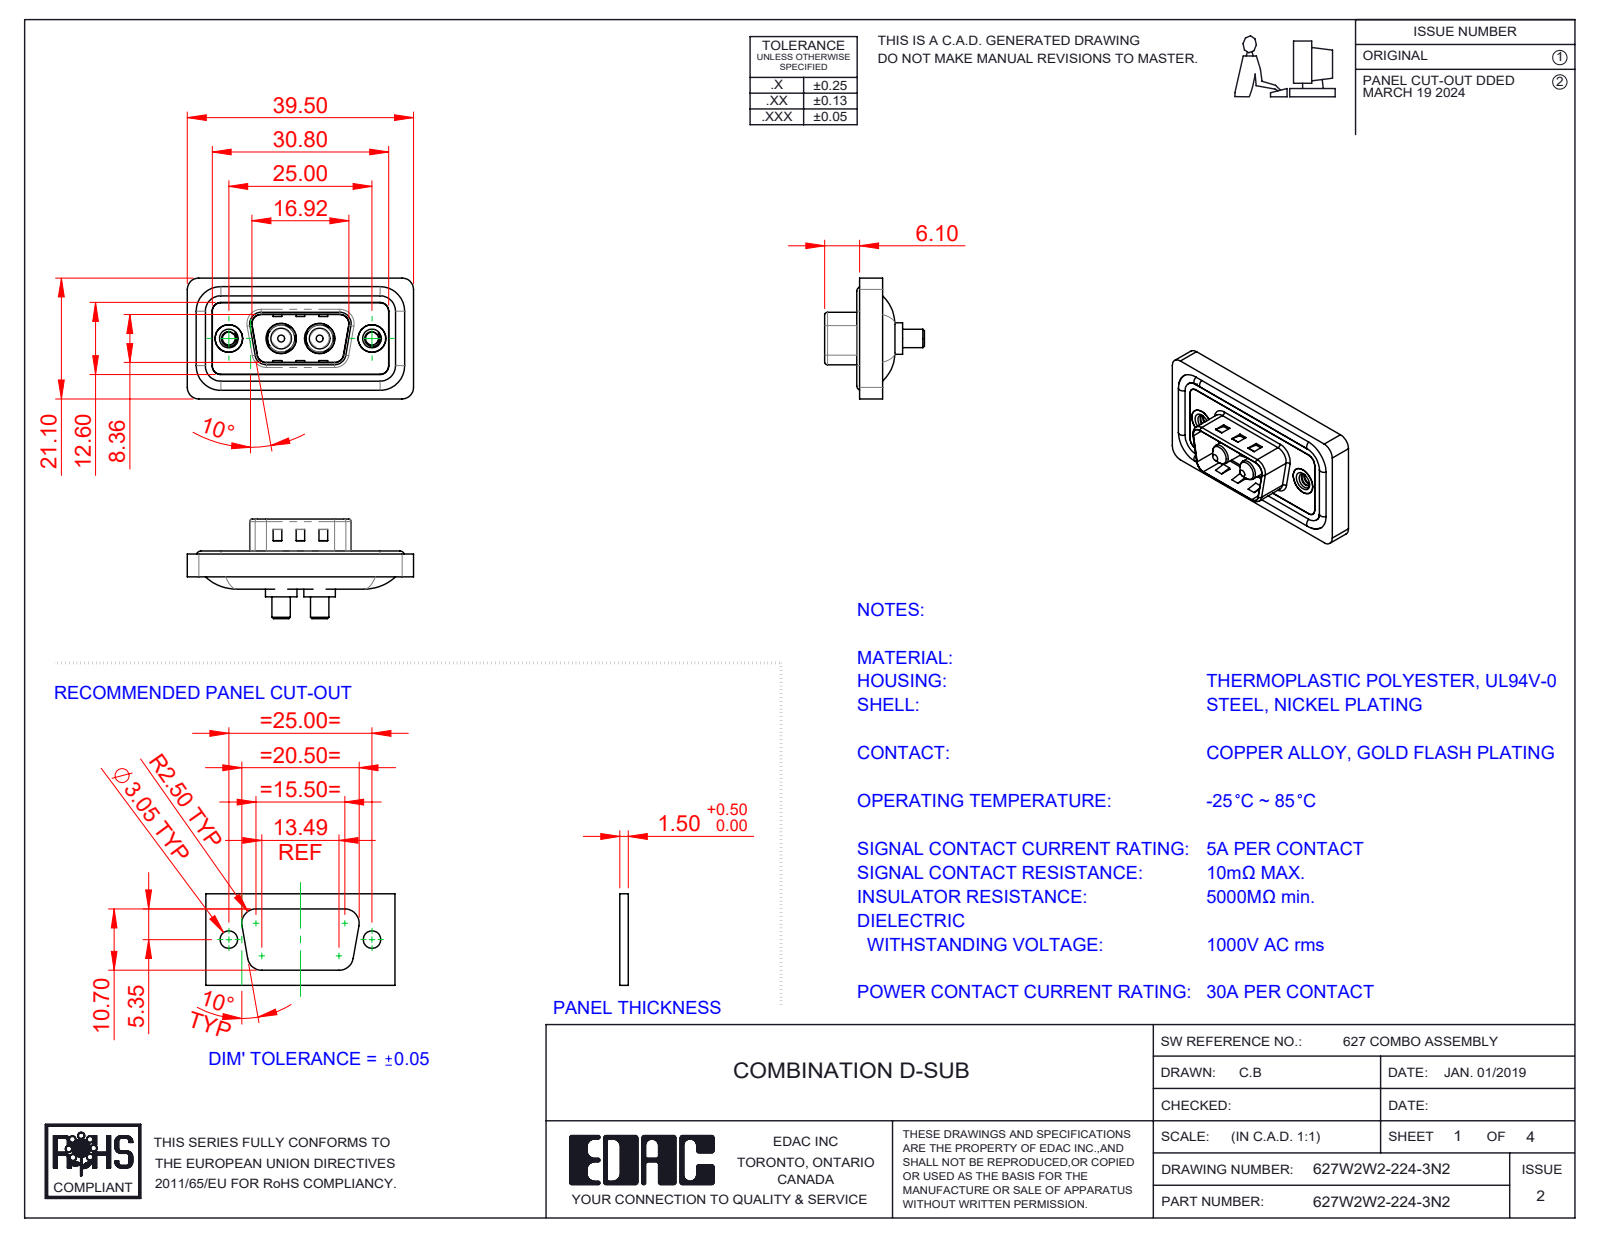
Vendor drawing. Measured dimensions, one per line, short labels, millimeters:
name: 627Combo Shell Rear_09 Contacts; 627W2W2-224-3N2; 627Combo Threaded Rivet_2; 627Combo Waterproof Housing_09 Contacts (+3 more)
written by: SolidWorks 2023 (CONFIG_CONTROL_DESIGN)
unit: mm
bodies: 11 solids, 489 faces (165 planar, 218 cylindrical, 106 other)
size: 39.5 × 21.1 × 17.4
volume: 4 475 mm³; area: 6 993 mm²
holes: 2× ⌀2.26, 2× ⌀4, 2× ⌀4.8, 2× ⌀4.85, 2× ⌀5, 2× ⌀5.3
bosses: 4× ⌀1.6, 2× ⌀5.5, 2× ⌀5.2, 2× ⌀4.9, 2× ⌀4.75, 2× ⌀3.75, 2× ⌀3.6, 2× ⌀3.2
rounds: 22× R1.5, 18× R2, 8× R0.5, 8× R1.6, 4× R0.25, 4× R0.6, 4× R0.65, 4× R0.9
face distances: 0.4, 1.1, 2.9, 3.1, 0.5, 1.6, 1.5, 4, 2.5, 0.7
hole spacings: 9.14, 15.86, 6.72, 25
